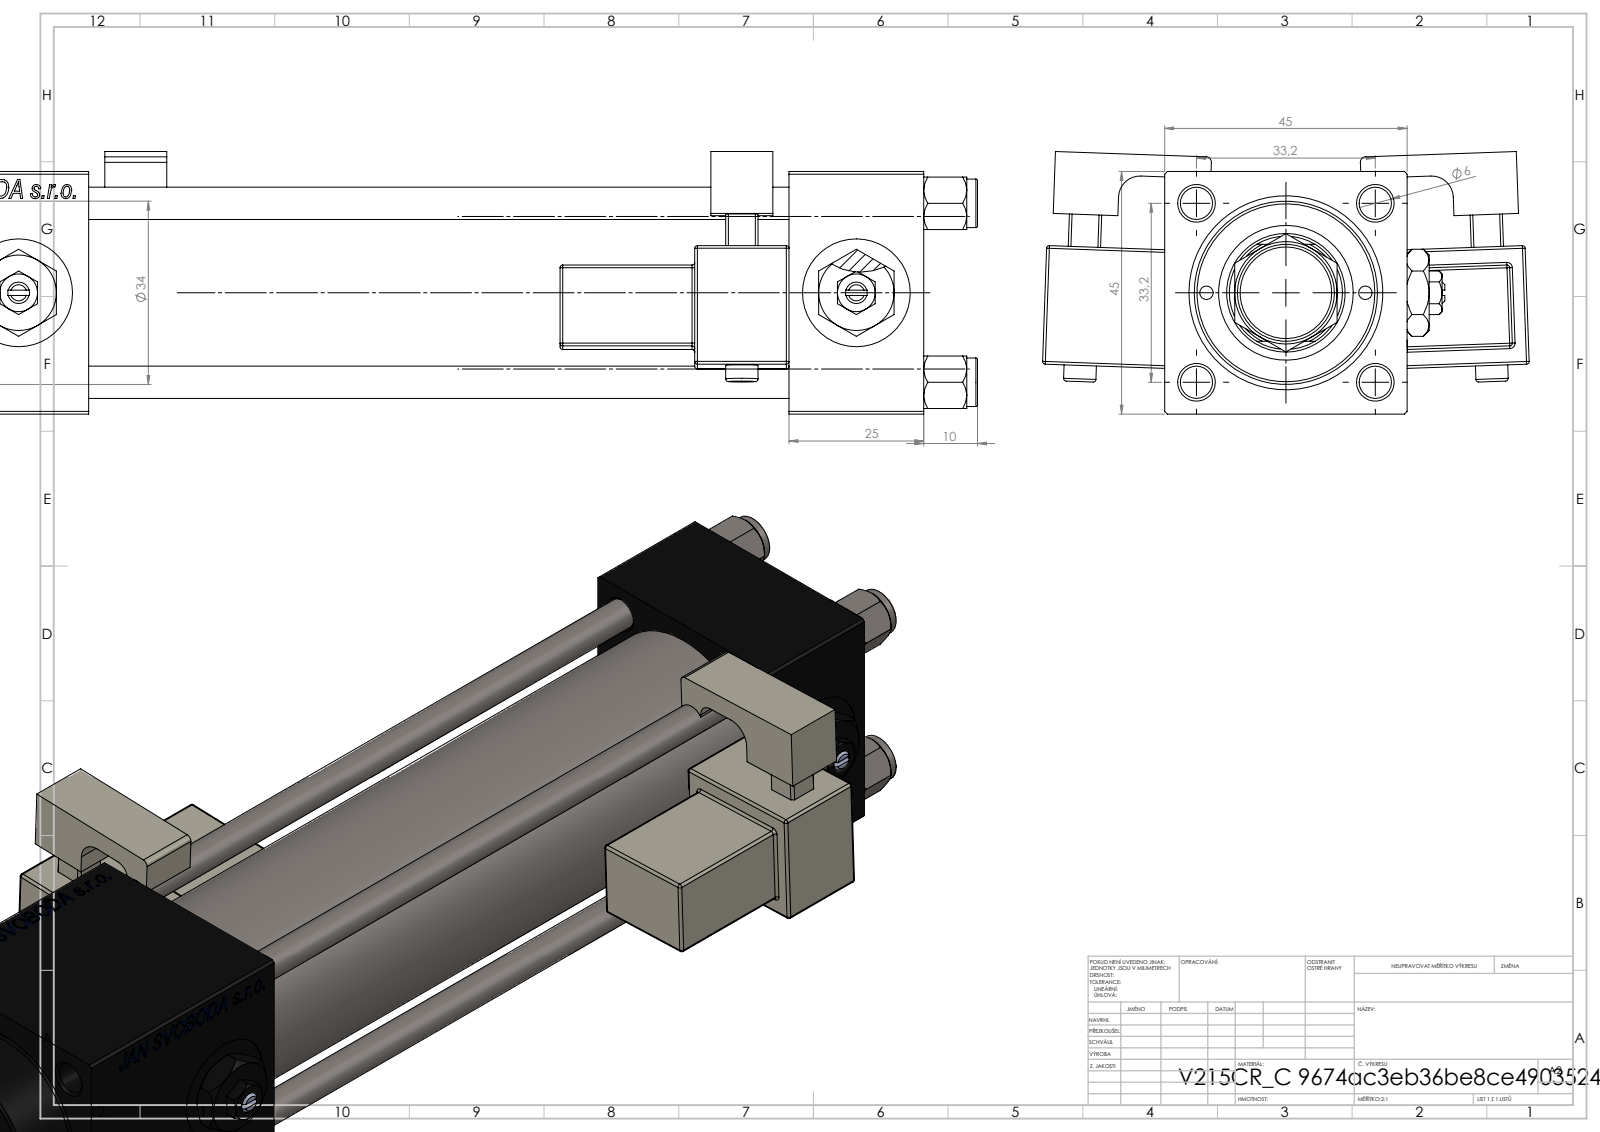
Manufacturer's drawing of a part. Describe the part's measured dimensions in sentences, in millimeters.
The part is named "MFA; V215CR_C_TYCINKA; NUT_M5_C; Zatka_pro_OIL_PORT (+4 more)". Its 3-D file was written by "SolidWorks 2019 (CONFIG_CONTROL_DESIGN)". It is 16 solids with 1464 faces: 652 planar, 166 cylindrical and 646 other. Overall it measures 271 by 90.31 by 48.72 millimeters. Its volume is 322 712 cubic millimeters and its surface area 117 262 square millimeters. Round holes: 4 of diameter 6, 2 of diameter 2.5, 2 of diameter 7, 2 of diameter 13.16, 2 of diameter 20, 1 of diameter 10.5, 1 of diameter 22, 1 of diameter 24, 1 of diameter 25, 1 of diameter 32, 1 of diameter 33. Round bosses or shafts: 4 of diameter 9, 2 of diameter 6, 1 of diameter 38, 1 of diameter 34, 1 of diameter 18, 1 of diameter 11. Partial cylindrical surfaces (rounded edges, fillets, slot ends): 48 of radius 0.5, 2 of radius 1, 2 of radius 2.5, 2 of radius 4, 1 of radius 10.5. The main face-to-face distances are 45, 25, 3, 155, 130, 203, 22.99, 112.5, 178, 44.8. The hole center spacings are 16.7, 23.48, 33.2, 35.47, 14.75, 46.95, 29.5, 155.5.
